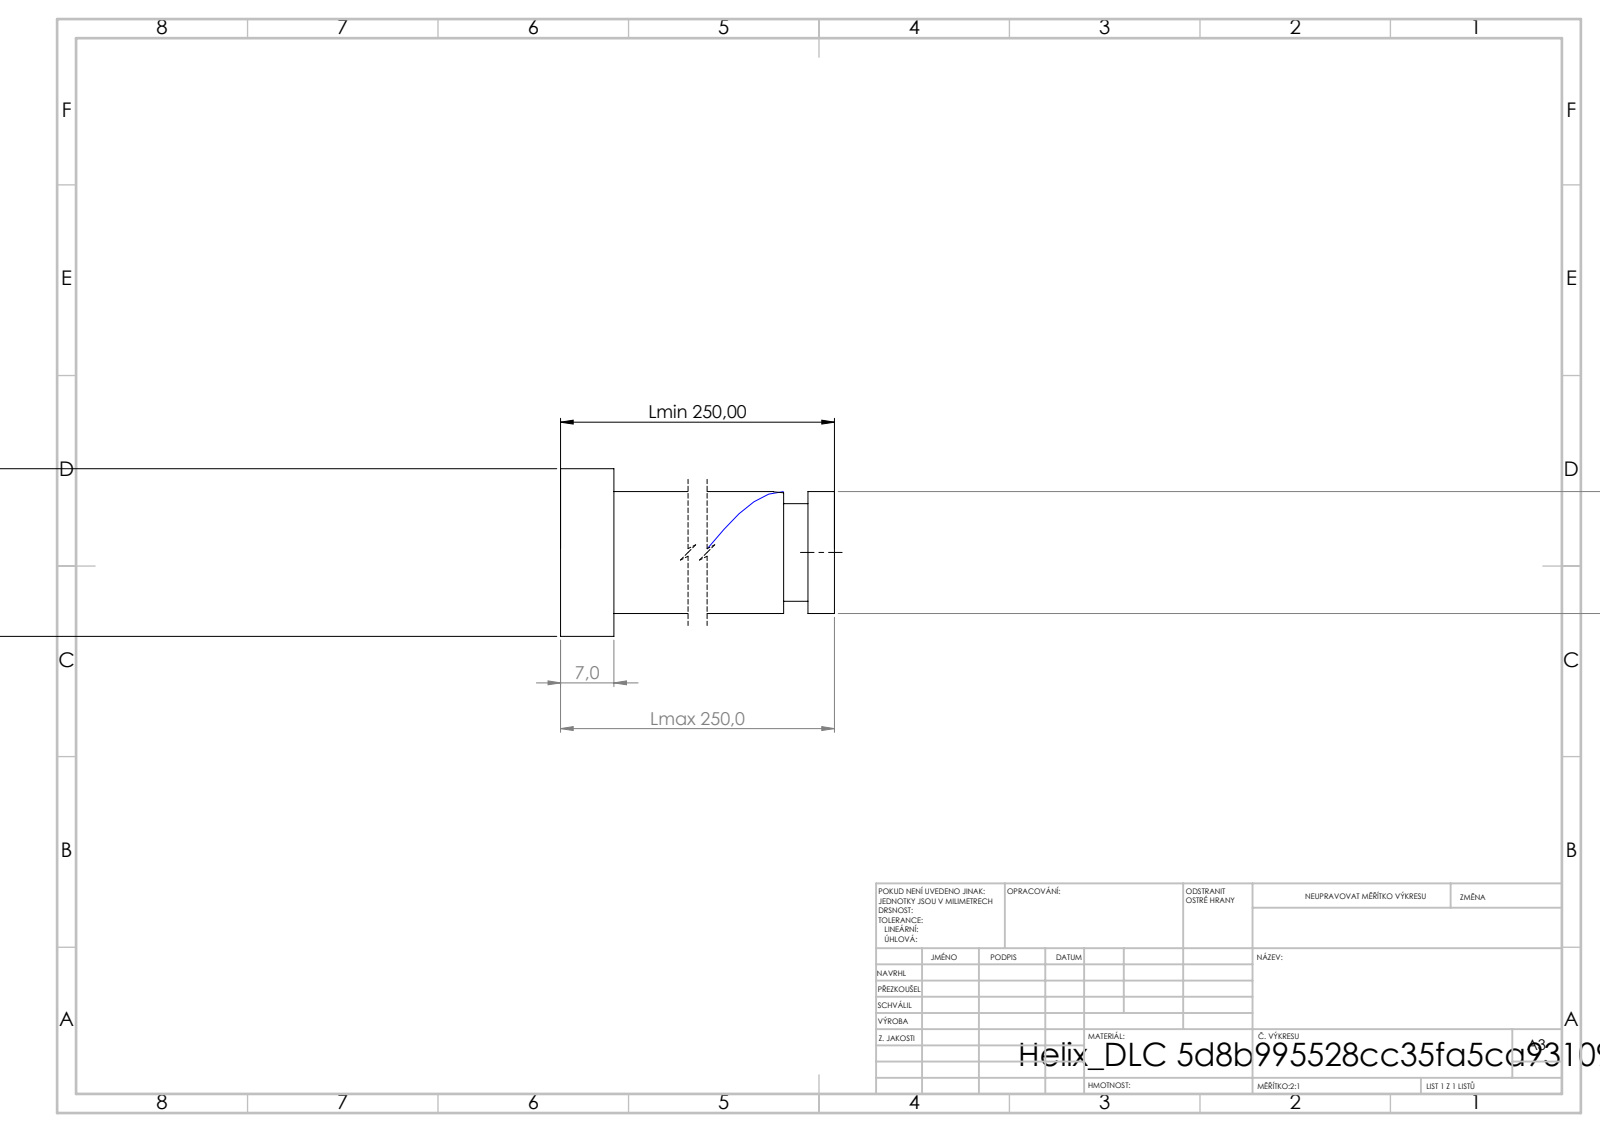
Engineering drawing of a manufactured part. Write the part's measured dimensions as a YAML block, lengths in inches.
step_written_by: "SolidWorks 2019 (CONFIG_CONTROL_DESIGN)"
units: inches
bodies: {solids: 1, faces: 21, planar: 6, cylindrical: 14, other: 1}
overall_size: [9.843, 0.866, 0.866]
volume: 3.1
surface_area: 21.58
round_bosses_or_shafts:
  - {diameter: 0.866, count: 1}
  - {diameter: 0.63, count: 1}
  - {diameter: 0.504, count: 1}
face_to_face_distances: [9.843, 0.276, 9.567, 9.706, 9.43, 0.137, 9.58, 9.304, 0.126, 0.263]
